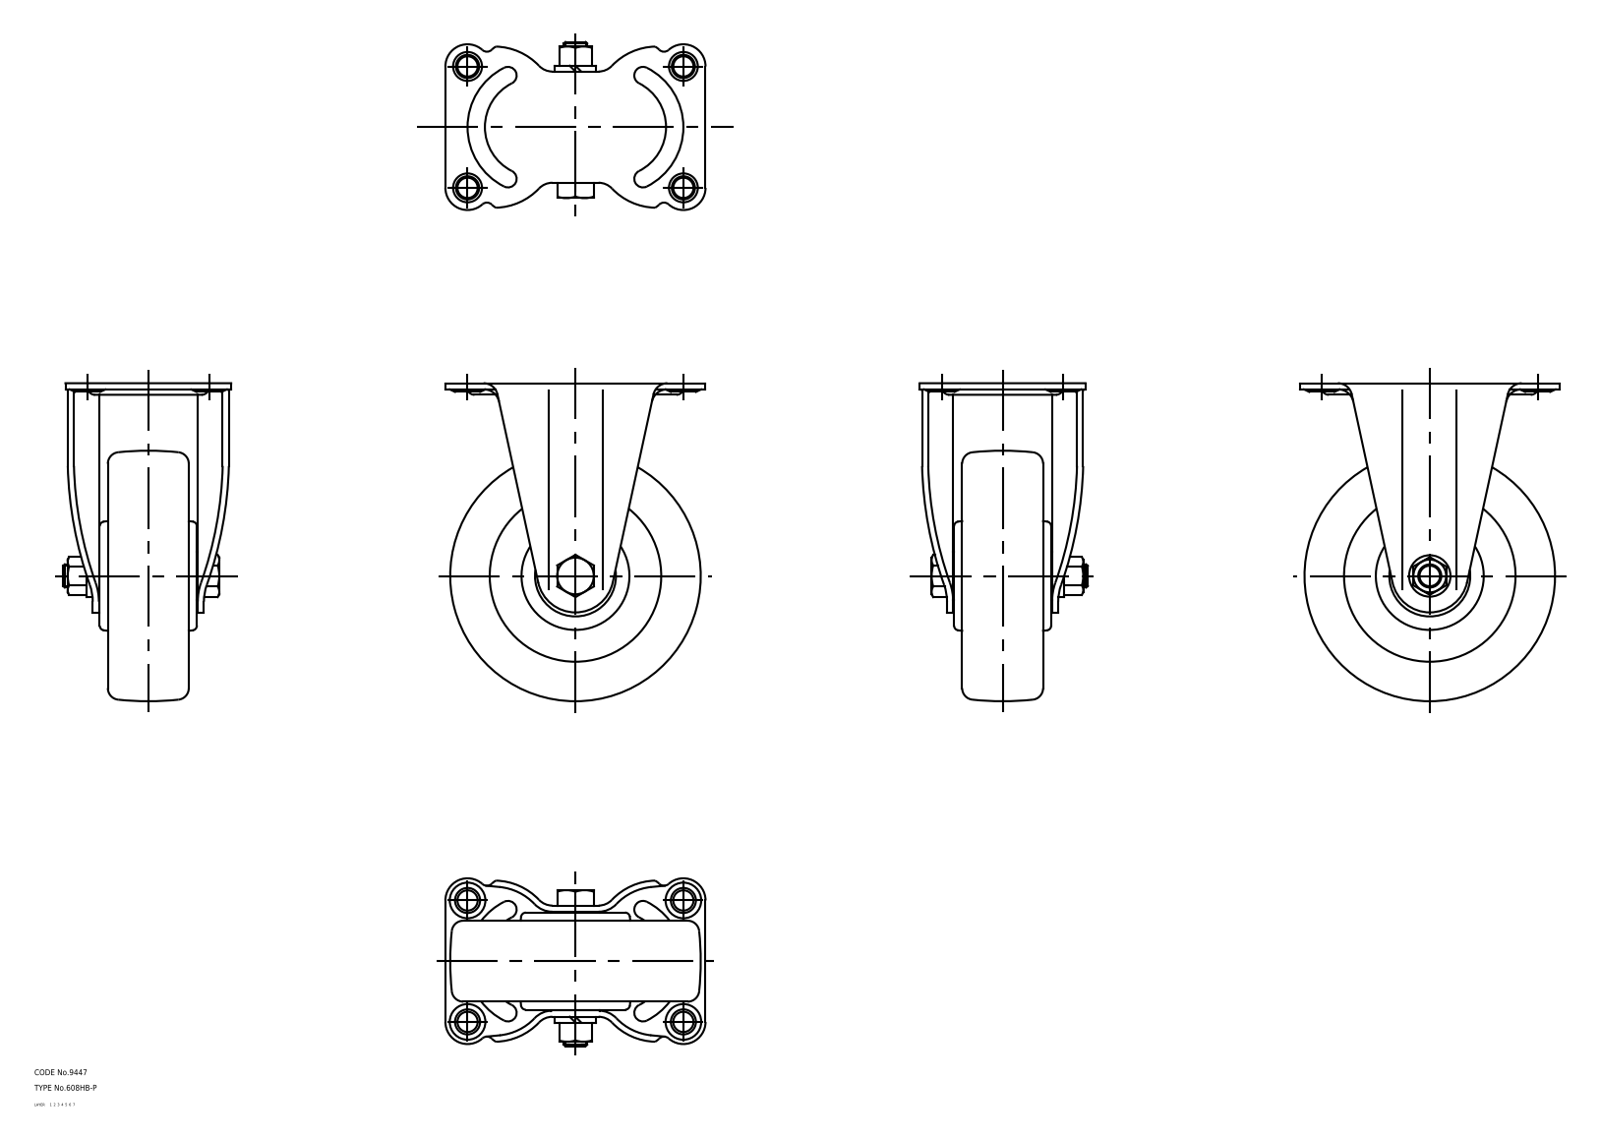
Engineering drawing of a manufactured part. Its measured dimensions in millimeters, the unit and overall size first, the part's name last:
Units: millimetres
Overall size (bounding box): 165 × 135 × 87.15
Volume: 590 598 mm³ · Surface area: 105 096 mm²
Bodies: 3 solids, 209 faces (0 planar, 0 cylindrical, 209 other)
Part name (STEP PRODUCT): 67122650; 67122663; 67122676
STEP written by: CADfix (AUTOMOTIVE_DESIGN)
